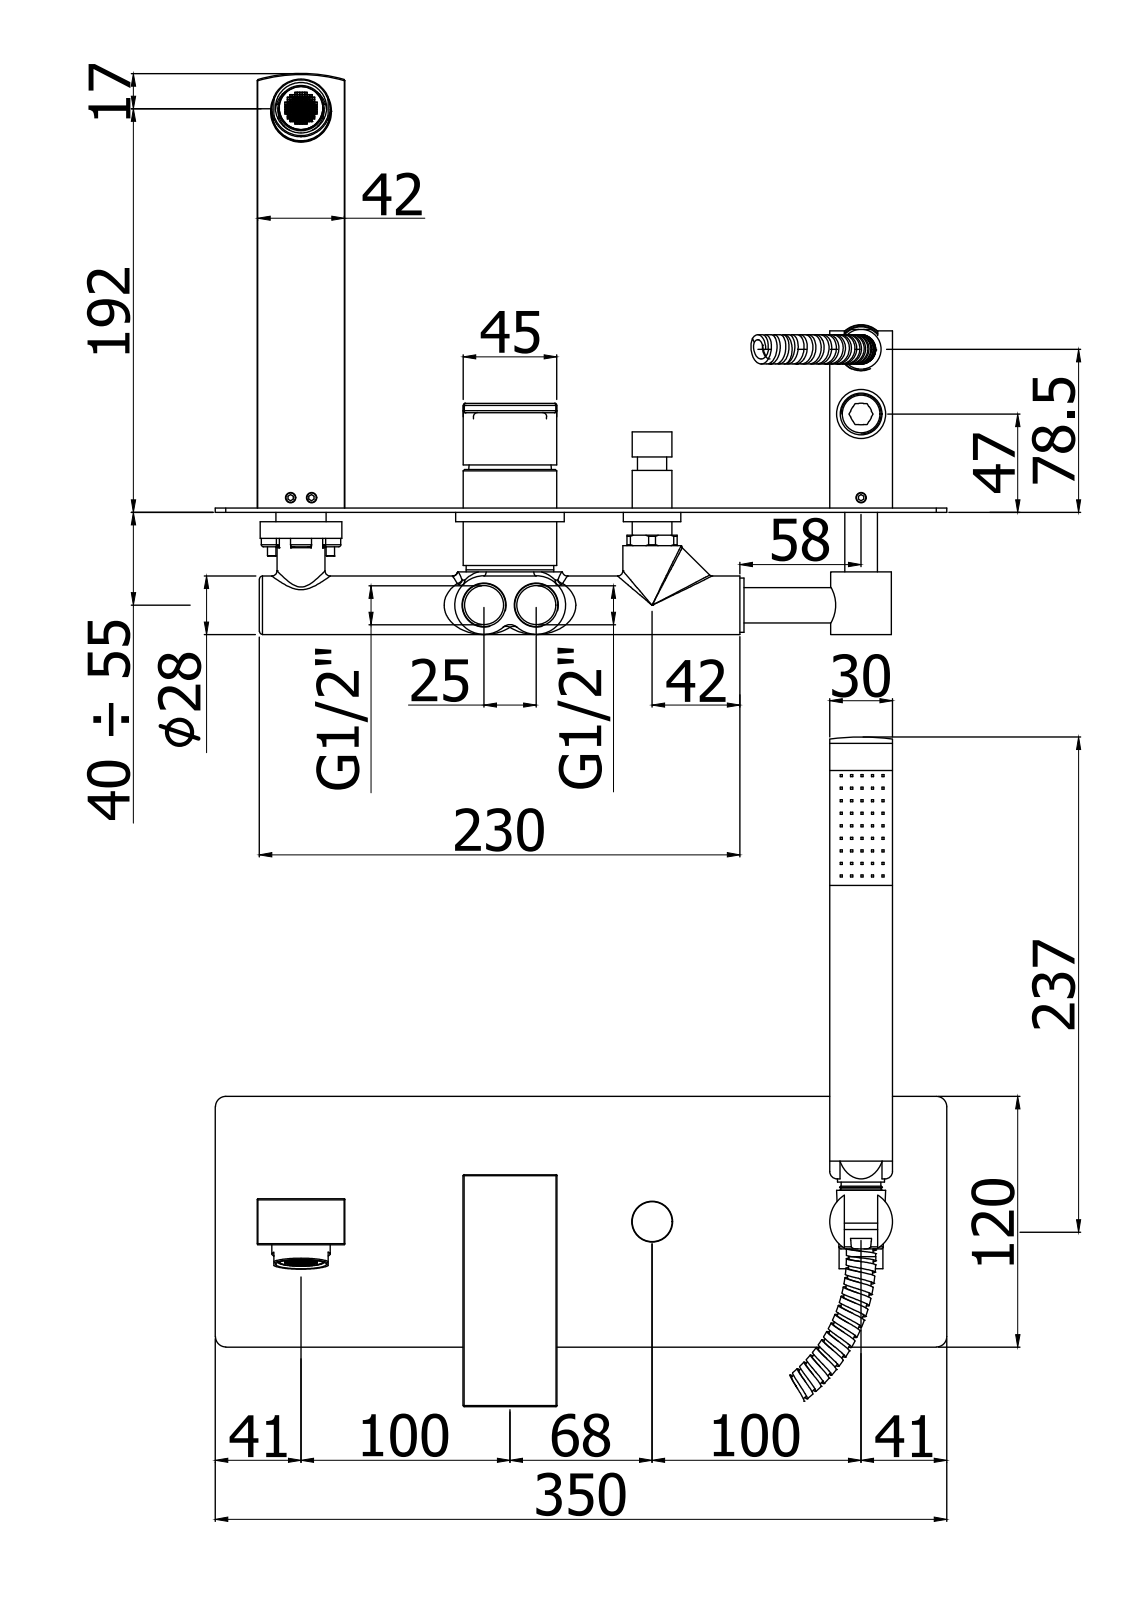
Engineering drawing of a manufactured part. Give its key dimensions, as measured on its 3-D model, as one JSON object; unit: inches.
{"part_name": "EL001CR", "step_written_by": "CREO PARAMETRIC BY PTC INC, 2020044 (CONFIG_CONTROL_DESIGN)", "units": "inches", "bodies": {"solids": 0, "faces": 252, "planar": 85, "cylindrical": 70, "other": 97}, "overall_size": [14.051, 12.965, 8.268], "round_holes": [[0.118, 1]], "round_bosses_or_shafts": [[1.764, 1], [1.181, 1], [1.102, 1], [0.906, 1], [0.886, 1], [0.823, 1], [0.736, 1], [0.732, 1]], "partial_cylinders_radius": [[0.059, 14], [0.02, 10], [0.157, 6], [0.079, 4], [11.811, 2], [0.108, 1], [0.925, 1], [2.953, 1]], "face_to_face_distances": [0.079, 0.866, 2.894, 2.815, 3.287, 3.209, 0.394, 1.654, 2.224, 1.181]}
